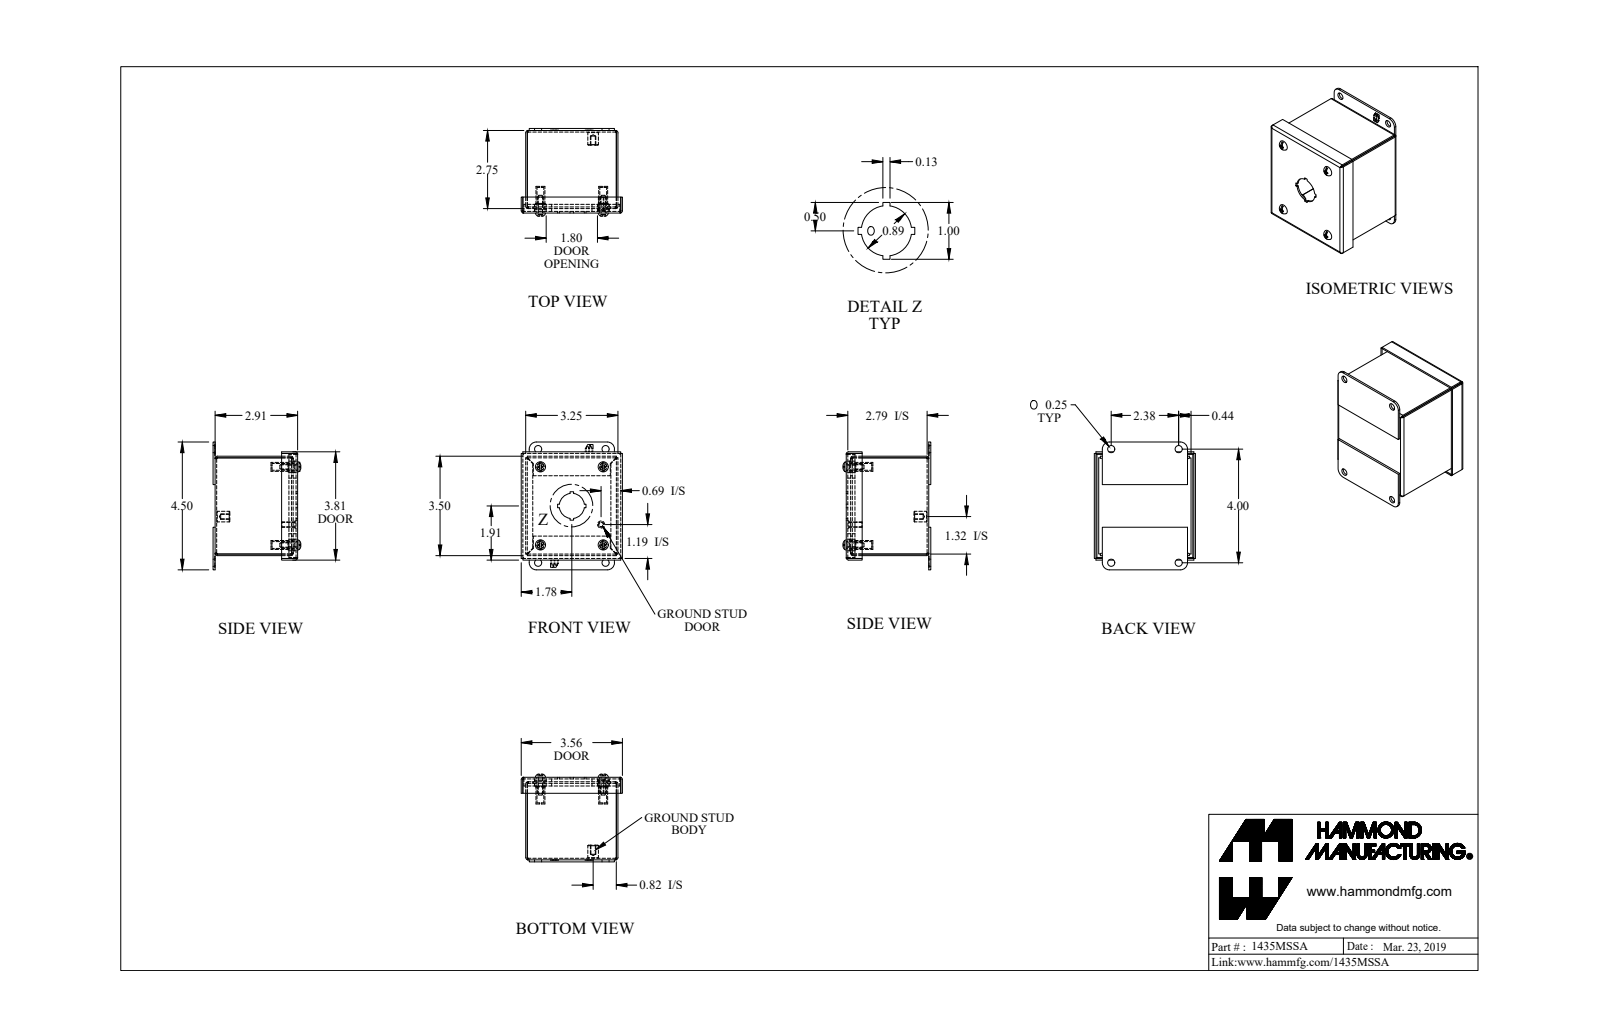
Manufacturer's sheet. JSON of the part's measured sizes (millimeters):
{"part_name": "1435MSSA_Default", "step_written_by": "SolidWorks 2019 (CONFIG_CONTROL_DESIGN)", "units": "millimeters", "bodies": {"solids": 19, "faces": 461, "planar": 295, "cylindrical": 136, "other": 30}, "overall_size": [114.3, 90.5, 78.5], "volume_mm3": 101700, "surface_area_mm2": 123700, "round_holes": [[6.4, 8], [1.7, 4], [6.1, 4], [6.4, 4], [10.3, 4], [4, 1], [22.5, 1]], "round_bosses_or_shafts": [[4.8, 5], [10.3, 4], [8, 4], [3.8, 4], [9.5, 1], [6.4, 1]], "partial_cylinders_radius": [[0.7, 12], [2.2, 12], [4.3, 4], [6.4, 4], [3.2, 2]], "face_to_face_distances": [1.4, 72.4, 1.4, 81.1, 87.5, 73.8, 70.9, 4, 75.7, 74.2], "hole_center_spacings": [56.2, 69.9, 16, 56.2, 69.9, 85.8, 89.6, 103.6]}
